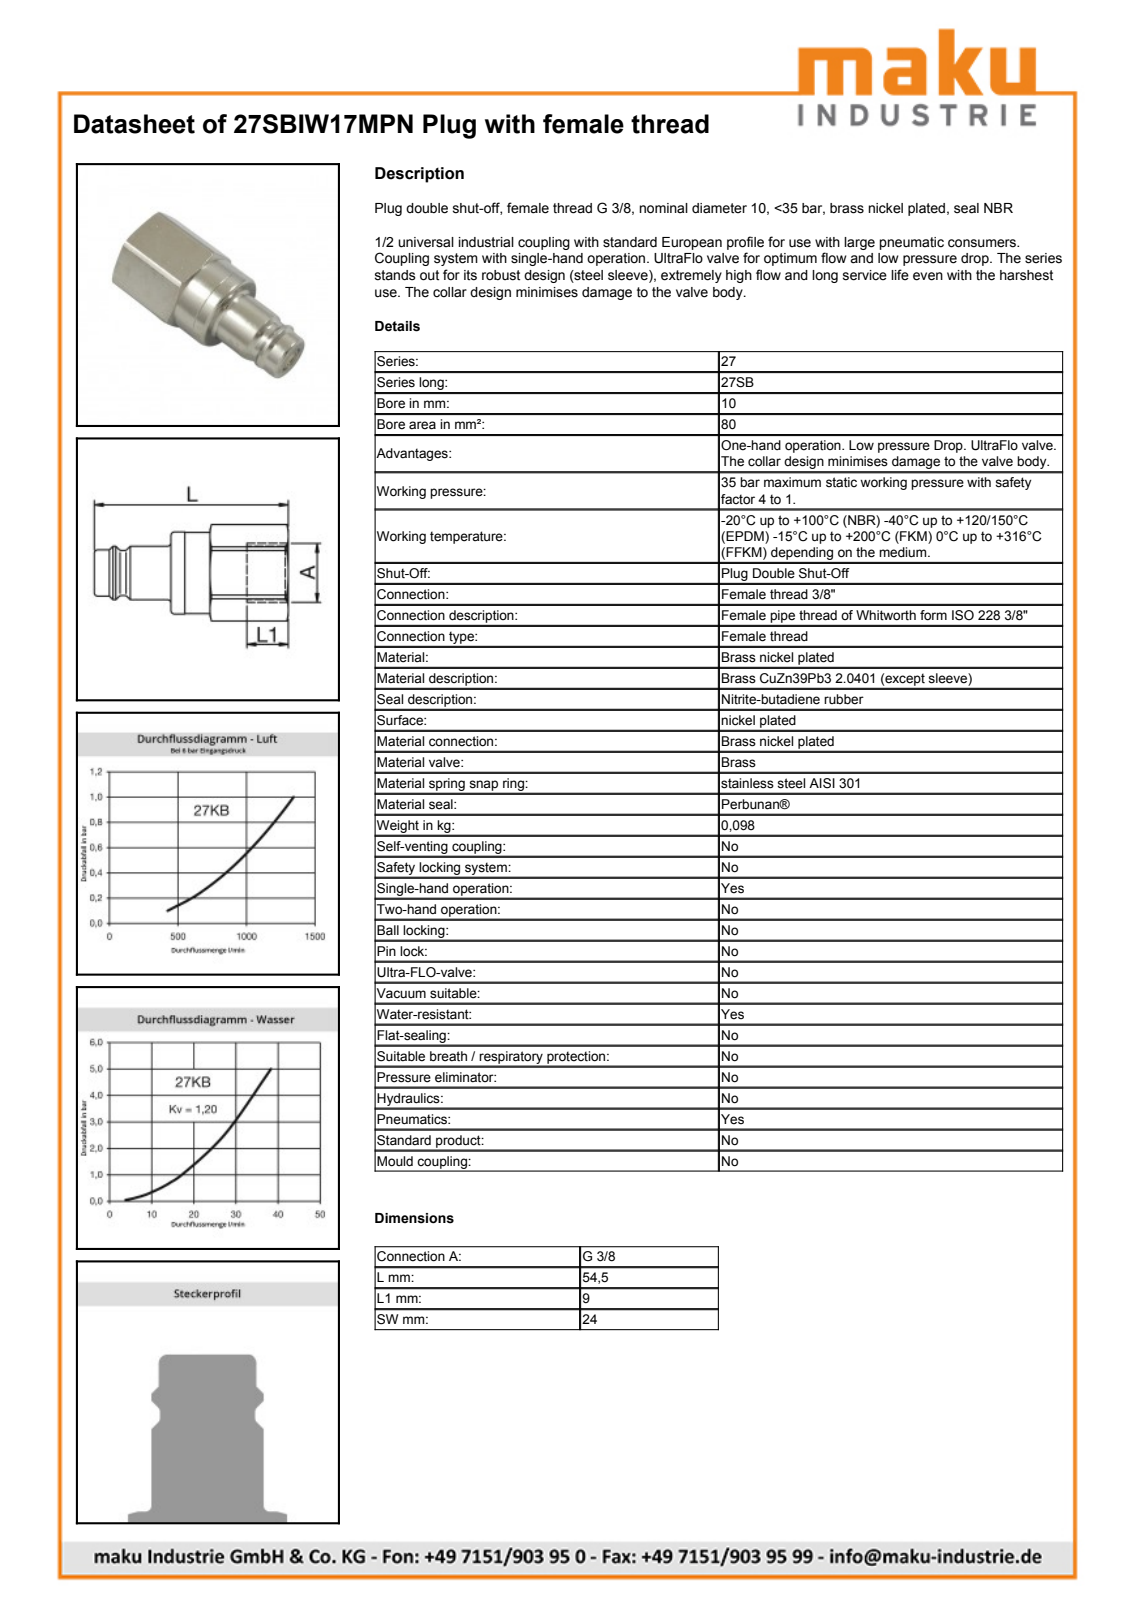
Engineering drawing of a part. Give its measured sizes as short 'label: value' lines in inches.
name: D107082
written by: Autodesk Inventor 2013 (AUTOMOTIVE_DESIGN)
unit: in
bodies: 1 solid, 52 faces (13 planar, 16 cylindrical, 23 other)
size: 2.142 × 1.047 × 1.031
volume: 1.03 in³; area: 8.088 in²
holes: 1× ⌀0.589, 1× ⌀0.748, 1× ⌀0.799
bosses: 1× ⌀0.906, 1× ⌀0.896, 1× ⌀0.728, 1× ⌀0.591, 1× ⌀0.512, 1× ⌀0.498
rounds: 1× R0.533
face distances: 0.945, 0.423, 0.872, 1.295, 0.846, 1.719, 2.142, 1, 0.154, 0.719
